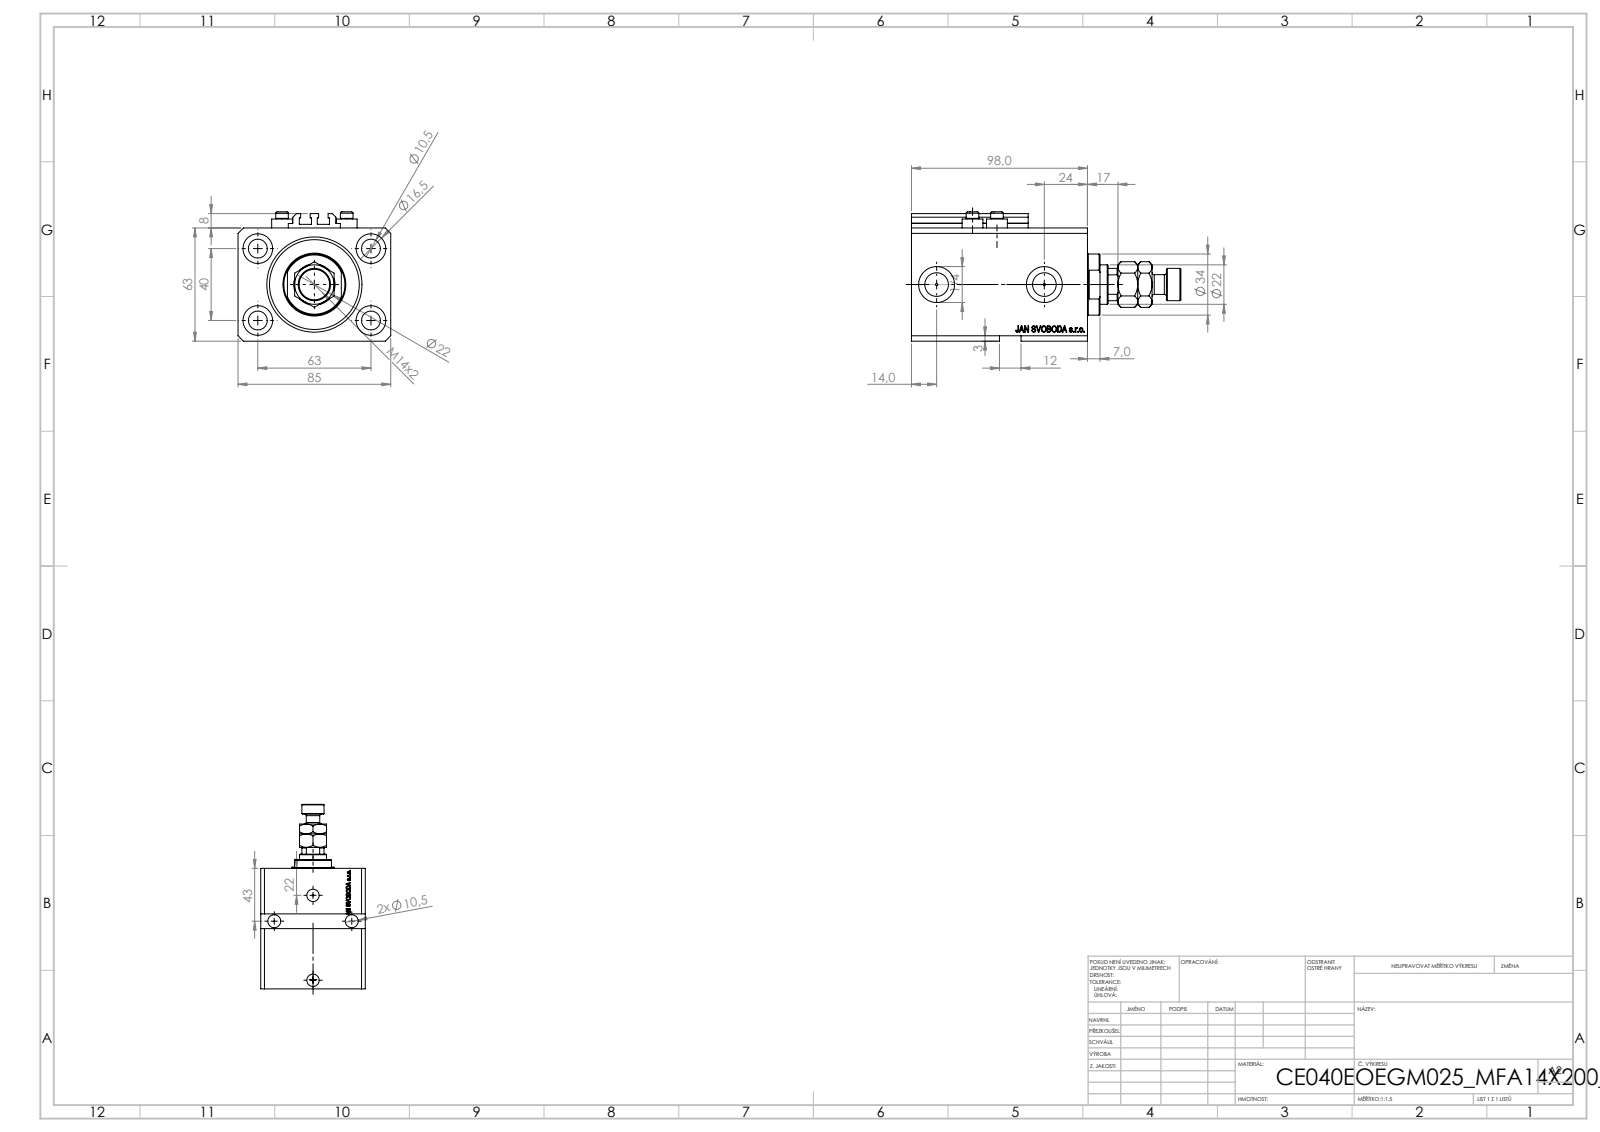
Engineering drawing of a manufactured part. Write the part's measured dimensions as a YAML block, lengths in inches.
part_name: "V250CE_VC_E; ALLEN BOLT V250CE; V250CE_C_VCP; MFA (+1 more)"
step_written_by: "SolidWorks 2019 (CONFIG_CONTROL_DESIGN)"
units: inches
bodies: {solids: 9, faces: 1139, planar: 551, cylindrical: 130, other: 458}
overall_size: [5.906, 3.346, 2.835]
volume: 28.63
surface_area: 159
round_holes:
  - {diameter: 0.413, count: 6}
  - {diameter: 0.049, count: 4}
  - {diameter: 0.157, count: 4}
  - {diameter: 0.65, count: 4}
  - {diameter: 0.394, count: 2}
  - {diameter: 0.518, count: 2}
  - {diameter: 0.787, count: 2}
  - {diameter: 0.492, count: 1}
  - {diameter: 0.866, count: 1}
  - {diameter: 1.575, count: 1}
  - {diameter: 2.087, count: 1}
round_bosses_or_shafts:
  - {diameter: 0.457, count: 4}
  - {diameter: 0.276, count: 4}
  - {diameter: 1.339, count: 1}
  - {diameter: 0.709, count: 1}
  - {diameter: 0.433, count: 1}
partial_cylinders:
  - {radius: 0.008, count: 10}
  - {radius: 0.413, count: 1}
face_to_face_distances: [2.48, 3.346, 0.669, 3.858, 3.189, 0.449, 2.74, 3.409, 0.118, 2.559]
hole_center_spacings: [1.469, 2.48, 0.535, 0.606, 0.983, 1.26, 1.278, 1.324]
